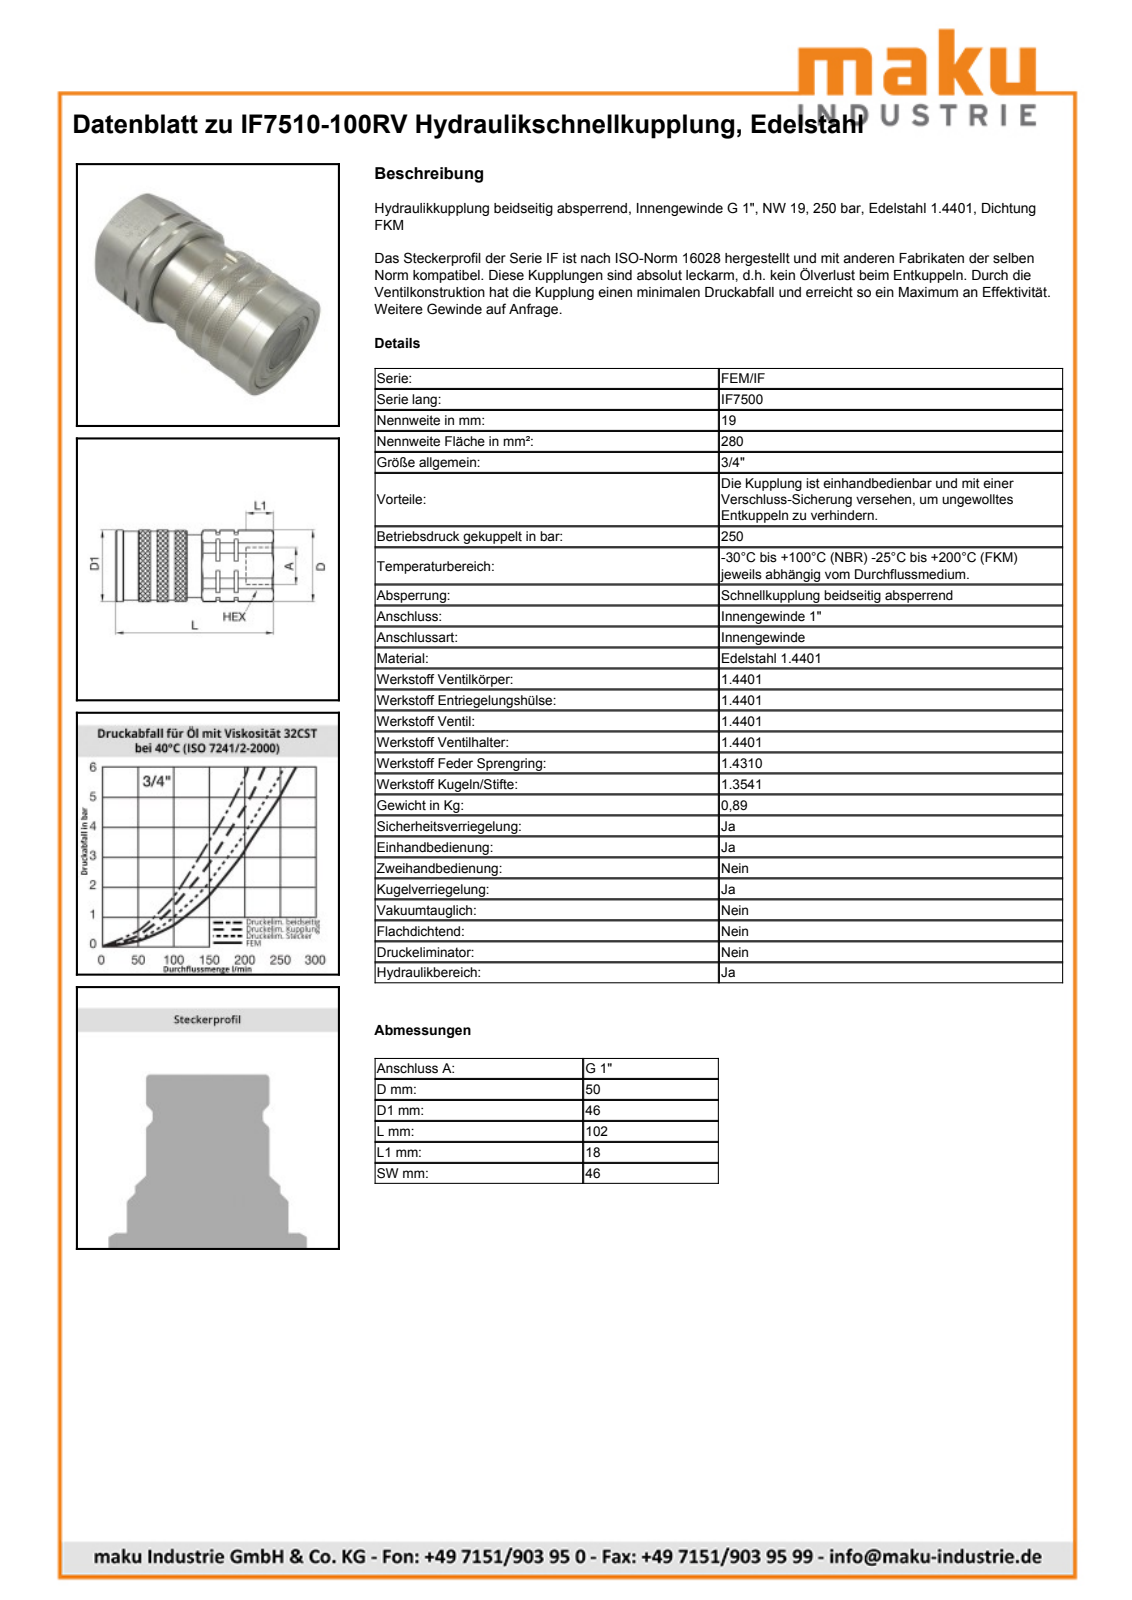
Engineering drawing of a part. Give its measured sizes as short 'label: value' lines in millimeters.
name: IF7510-100RV
written by: SolidWorks 2009 (AUTOMOTIVE_DESIGN)
unit: mm
bodies: 1 solid, 175 faces (50 planar, 73 cylindrical, 52 other)
size: 101 × 50 × 46
volume: 148 348 mm³; area: 22 136 mm²
holes: 1× ⌀20.7, 1× ⌀30.06, 1× ⌀30.29, 1× ⌀36.7, 1× ⌀41.3, 1× ⌀42.2
bosses: 1× ⌀46, 1× ⌀45, 1× ⌀42, 1× ⌀41, 1× ⌀36.5, 1× ⌀29.8, 1× ⌀20.5
rounds: 2× R0.5, 1× R21.49, 1× R23.5, 1× R25
face distances: 46, 101, 100.5, 0.5, 23.24, 77.26, 77.76, 41, 60, 17.76
